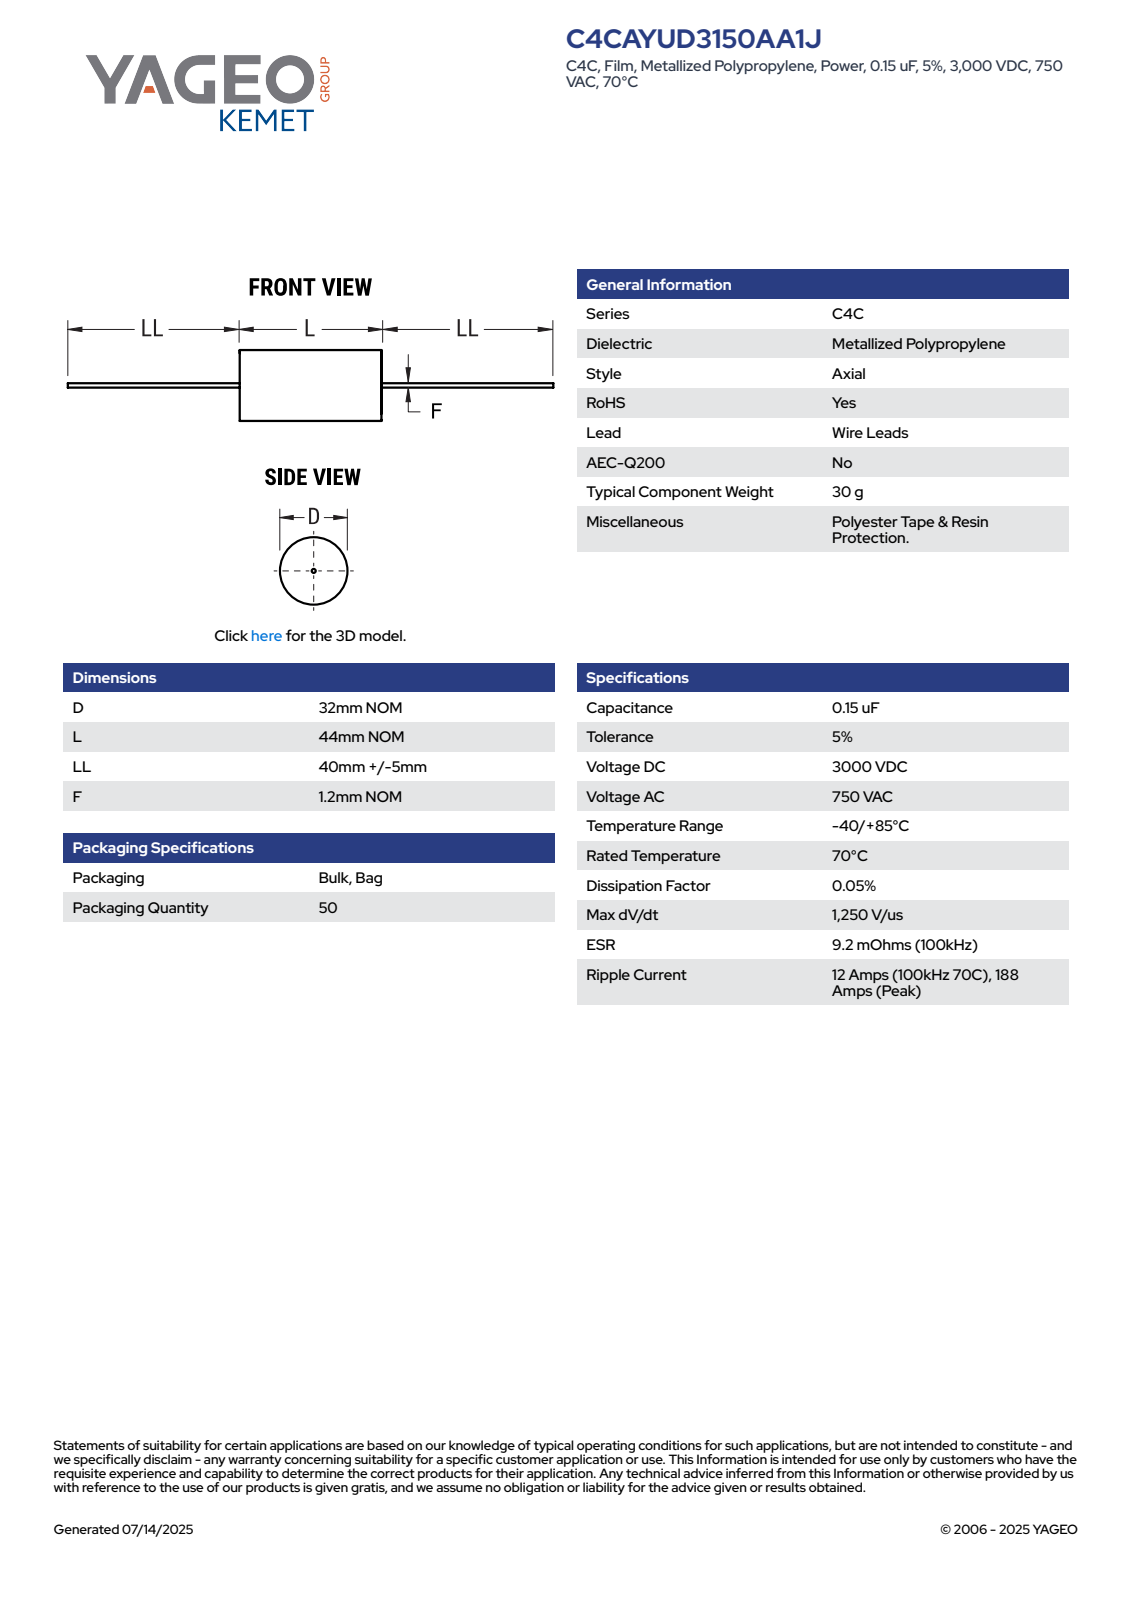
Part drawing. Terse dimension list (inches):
name: CFP_ACWF_32X44_D32L44LL45F1.2
written by: SolidWorks 2014 (AUTOMOTIVE_DESIGN)
unit: in
bodies: 2 solids, 87 faces (28 planar, 28 cylindrical, 31 other)
size: 5.276 × 1.26 × 1.26
volume: 2.166 in³; area: 12.37 in²
bosses: 1× ⌀1.26, 1× ⌀0.047
rounds: 1× R0.63
face distances: 1.732, 1.732, 1.771, 1.772, 3.504, 5.276, 3.504, 3.504, 1.772
